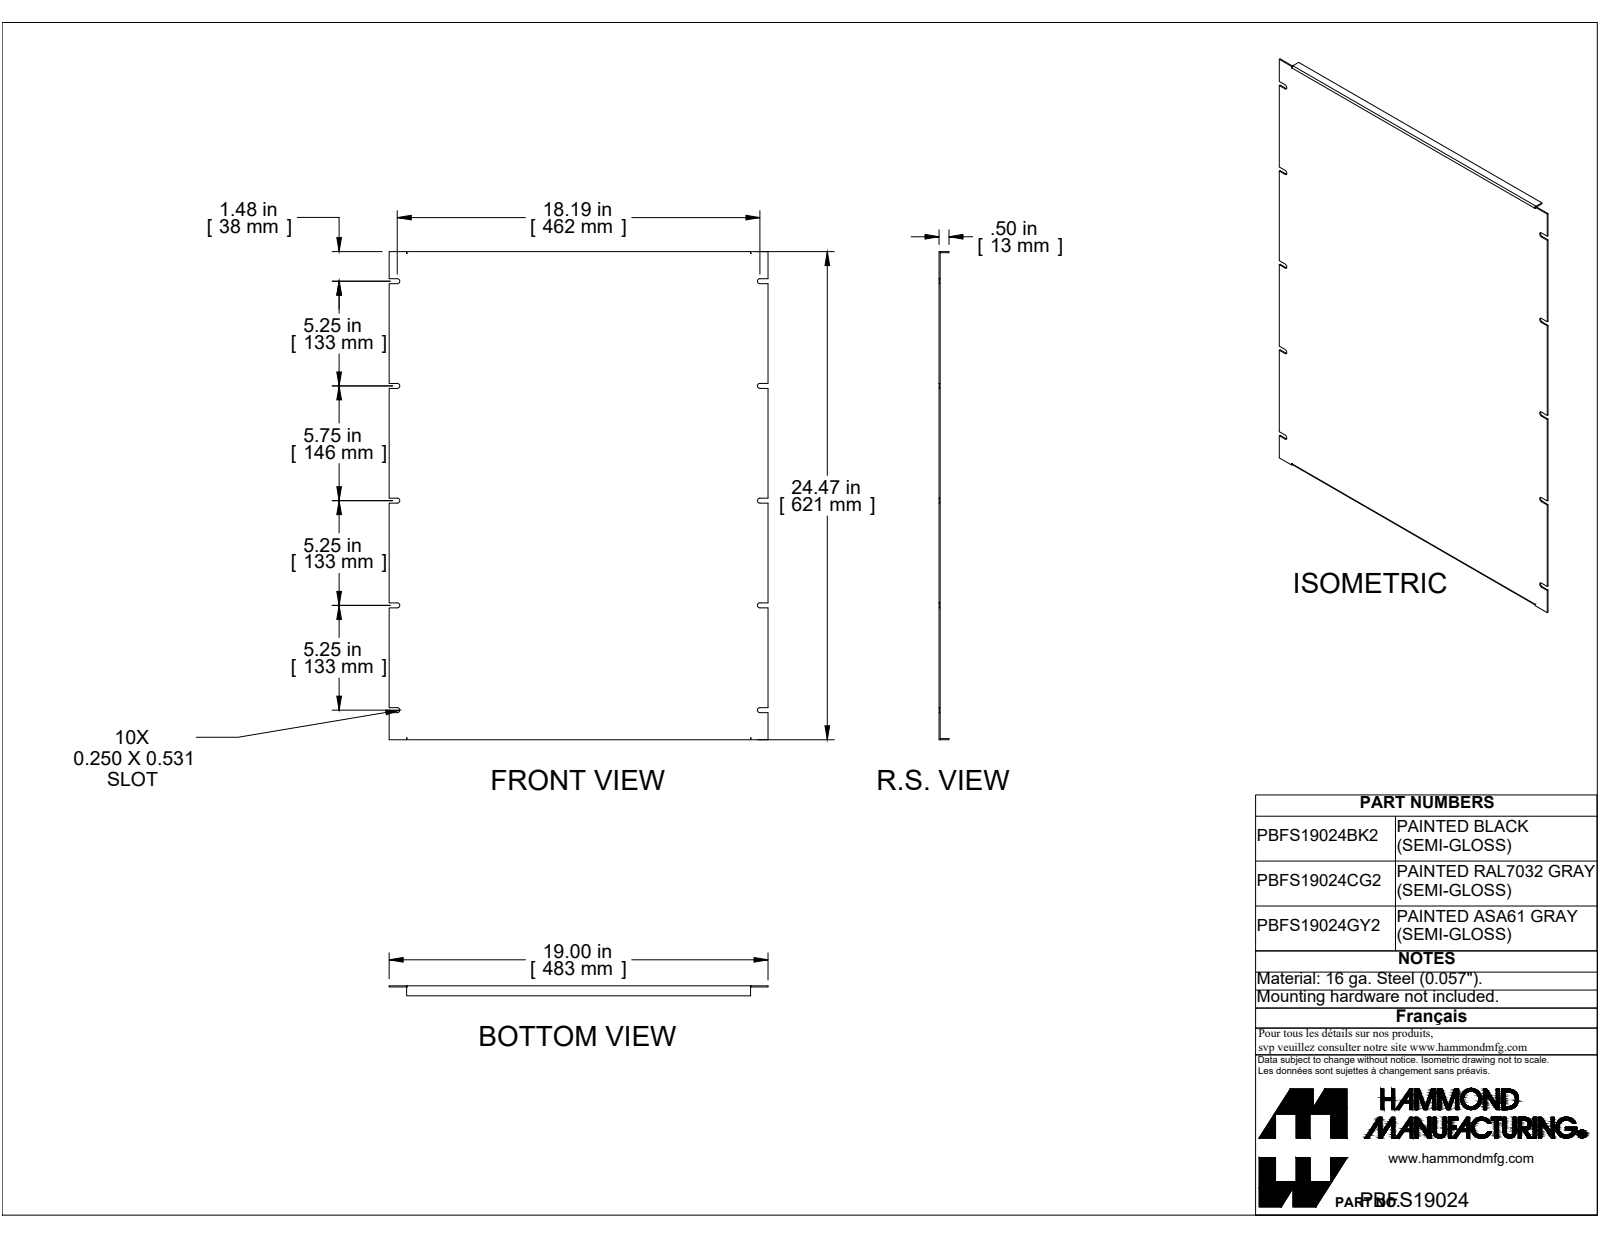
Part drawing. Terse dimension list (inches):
name: PBFS19024
written by: SolidWorks 2019 (CONFIG_CONTROL_DESIGN)
unit: in
bodies: 1 solid, 70 faces (56 planar, 14 cylindrical, 0 other)
size: 24.468 × 19 × 0.5
volume: 27.25 in³; area: 961.8 in²
rounds: 10× R0.125, 2× R0.029, 2× R0.086
face distances: 0.057, 0.057, 24.411, 24.468, 24.354, 0.5, 0.443, 19, 5.25, 0.25
